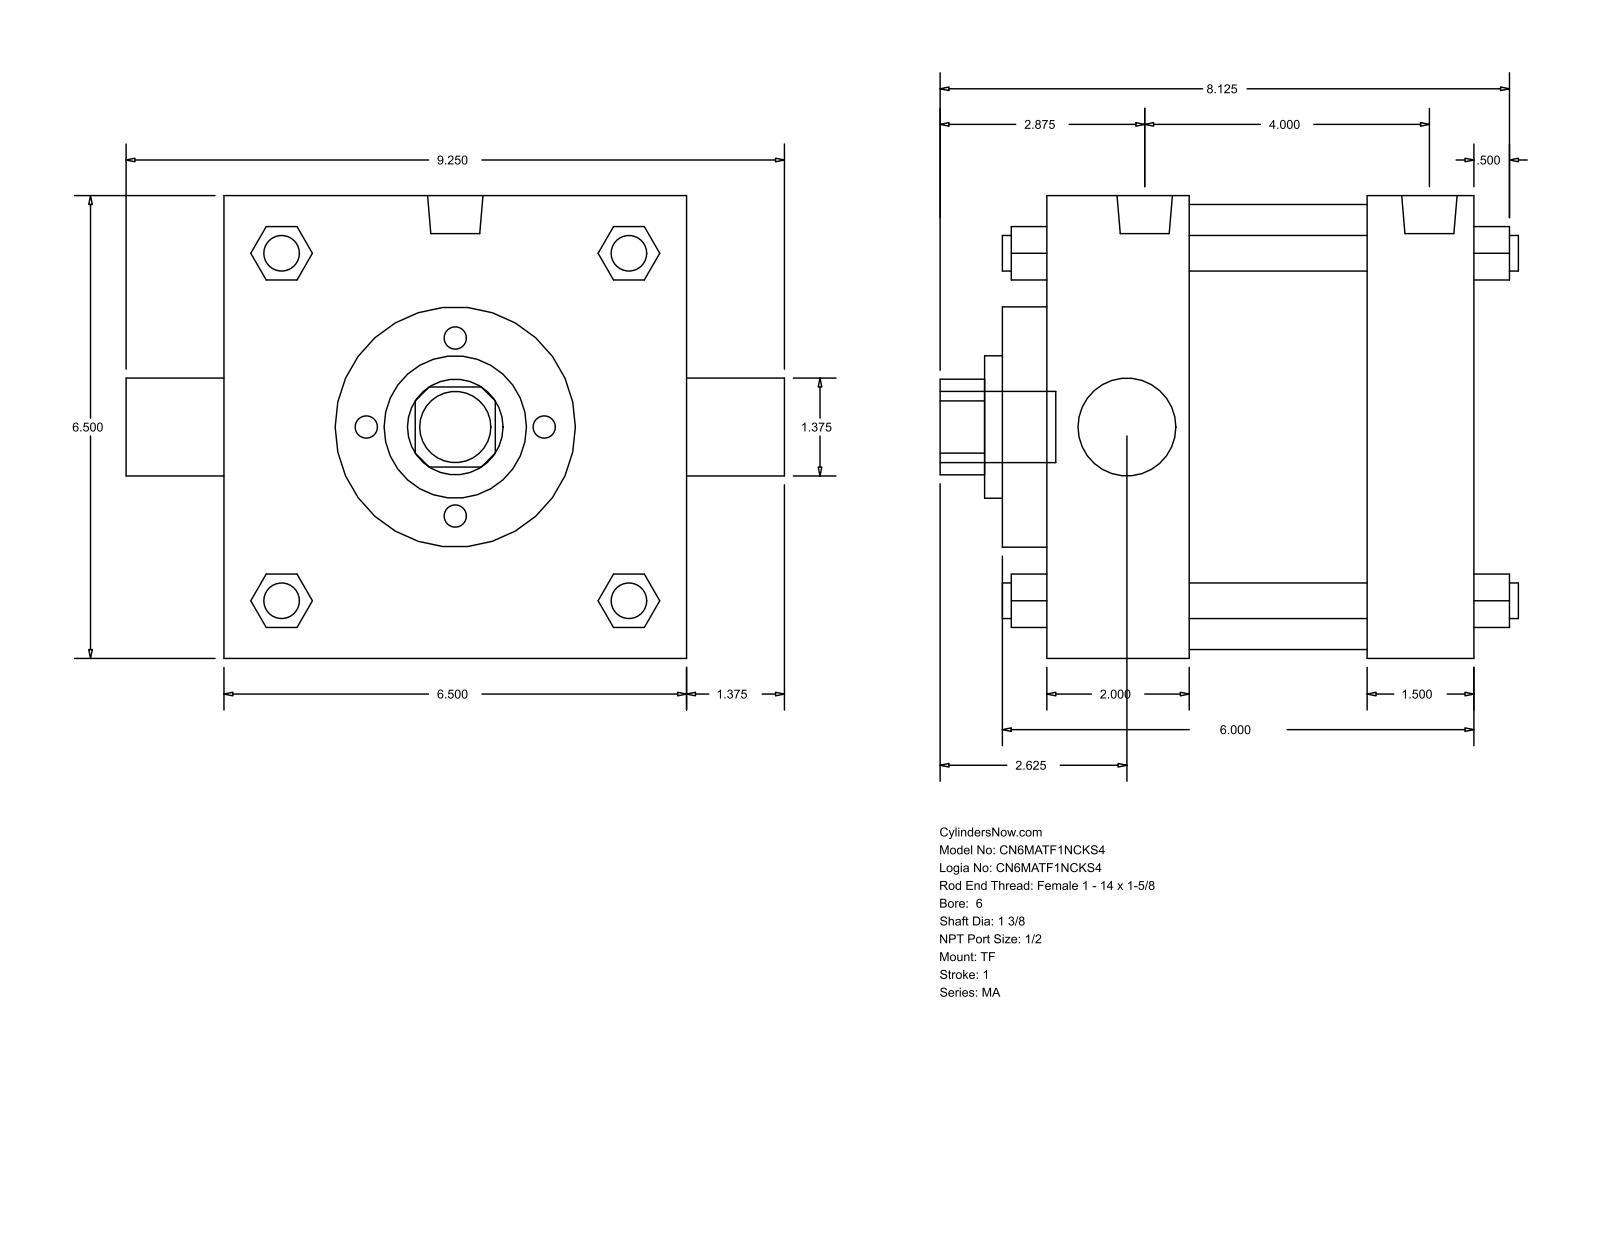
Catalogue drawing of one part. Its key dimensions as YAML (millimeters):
part_name: "MA_TF__0600_1.375"
step_written_by: "GSSL Pune (CONFIG_CONTROL_DESIGN)"
units: millimeters
bodies: {solids: 0, faces: 122, planar: 93, cylindrical: 29, other: 0}
overall_size: [234.95, 206.38, 165.1]
round_holes:
  - {diameter: 34.92, count: 2}
  - {diameter: 50.8, count: 1}
  - {diameter: 85.72, count: 1}
  - {diameter: 158.75, count: 1}
round_bosses_or_shafts:
  - {diameter: 12.7, count: 4}
  - {diameter: 17.46, count: 3}
  - {diameter: 19.77, count: 2}
  - {diameter: 25.4, count: 1}
partial_cylinders:
  - {radius: 17.06, count: 1}
face_to_face_distances: [165.1, 155.58, 66.67, 50.8, 104.78, 117.47, 38.11, 15.87, 133.34, 171.45]
